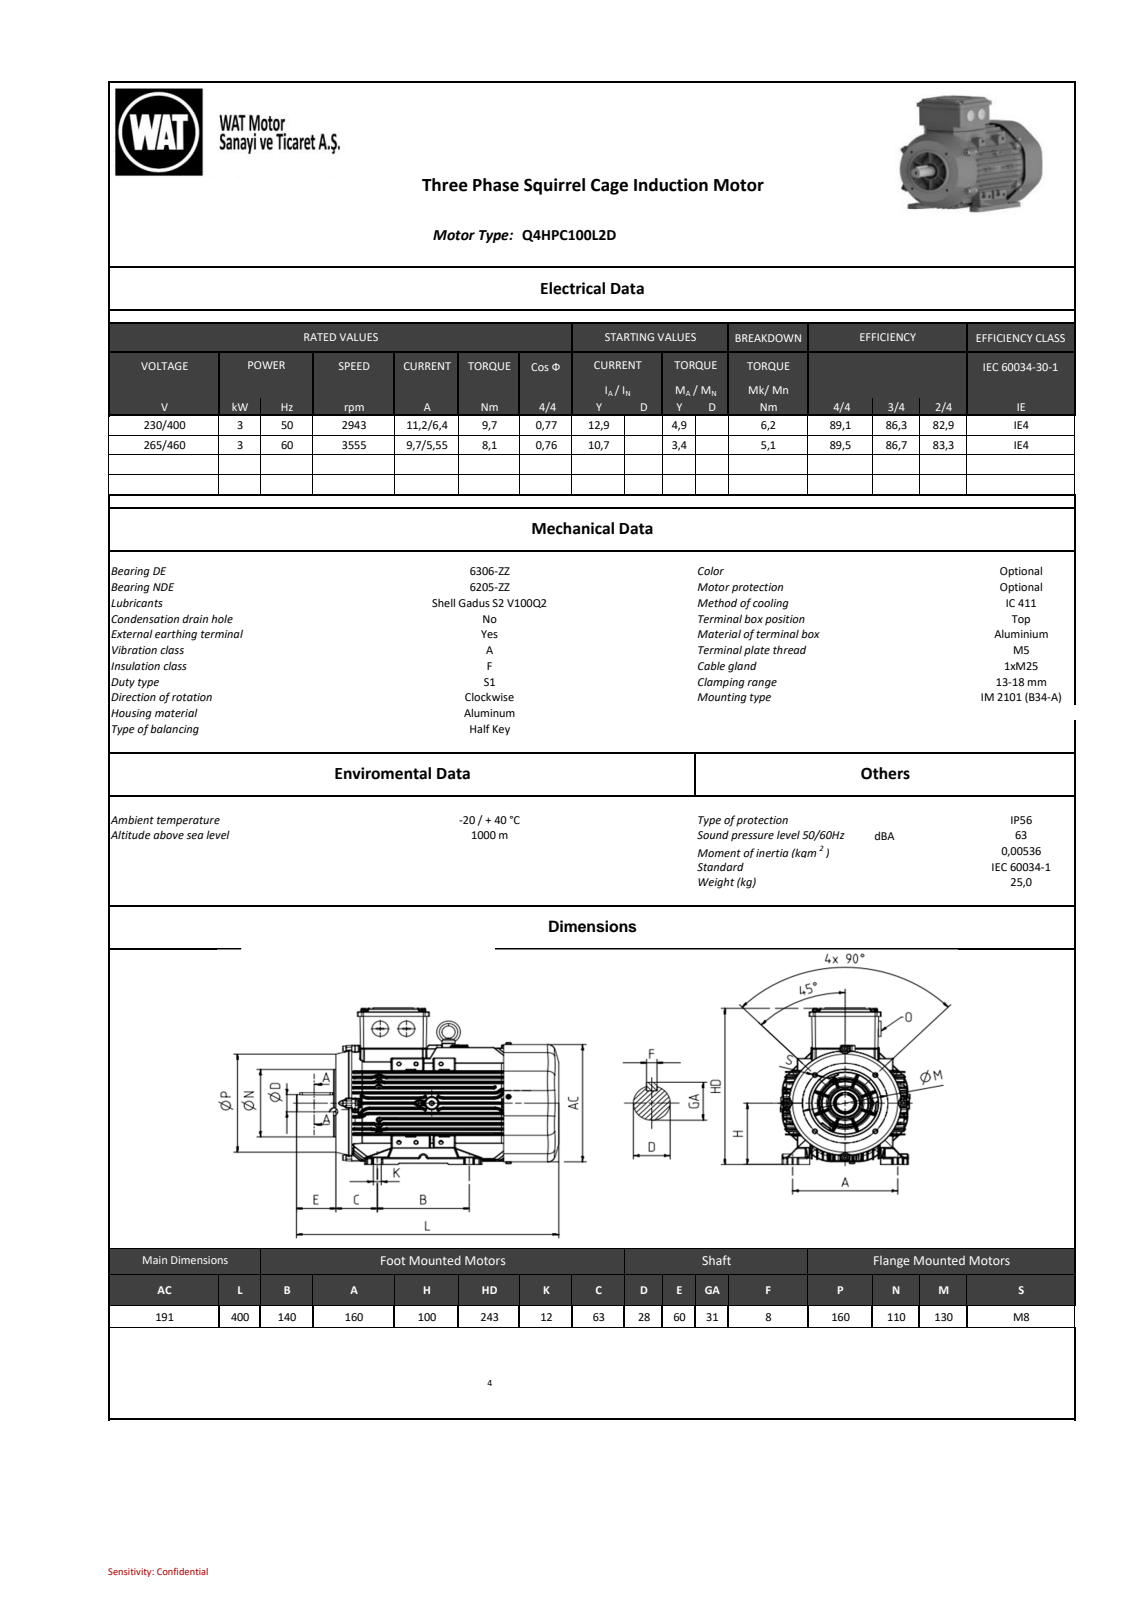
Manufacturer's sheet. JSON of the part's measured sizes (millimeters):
{"part_name": "QH series_ 100_B34a_stp_objects", "step_written_by": "SIEMENS PLM Software NX2206.8101 (AUTOMOTIVE_DESIGN)", "units": "millimeters", "bodies": {"solids": 0, "faces": 6093, "planar": 1364, "cylindrical": 2449, "other": 2280}, "overall_size": [399.31, 255.72, 197.75], "round_holes": [[6.5, 4], [6.8, 4], [10, 1], [44.42, 1], [57.4, 1], [89, 1], [109, 1], [129, 1], [133, 1]], "round_bosses_or_shafts": [[8, 8], [12, 4], [8.5, 4], [6, 4], [5, 4], [25, 3], [113.5, 1], [110, 1]], "partial_cylinders_radius": [[0.8, 671], [1, 523], [2, 125], [1.5, 82], [0.5, 57], [0.81, 50], [5, 40], [15, 26]], "face_to_face_distances": [8.53, 8.46, 8.45, 76.24, 16.91, 93.45, 25.58, 17.05, 76.68, 59.63], "hole_center_spacings": [65, 91.92, 64, 66.62, 104.41, 128, 129.99, 143.11]}
